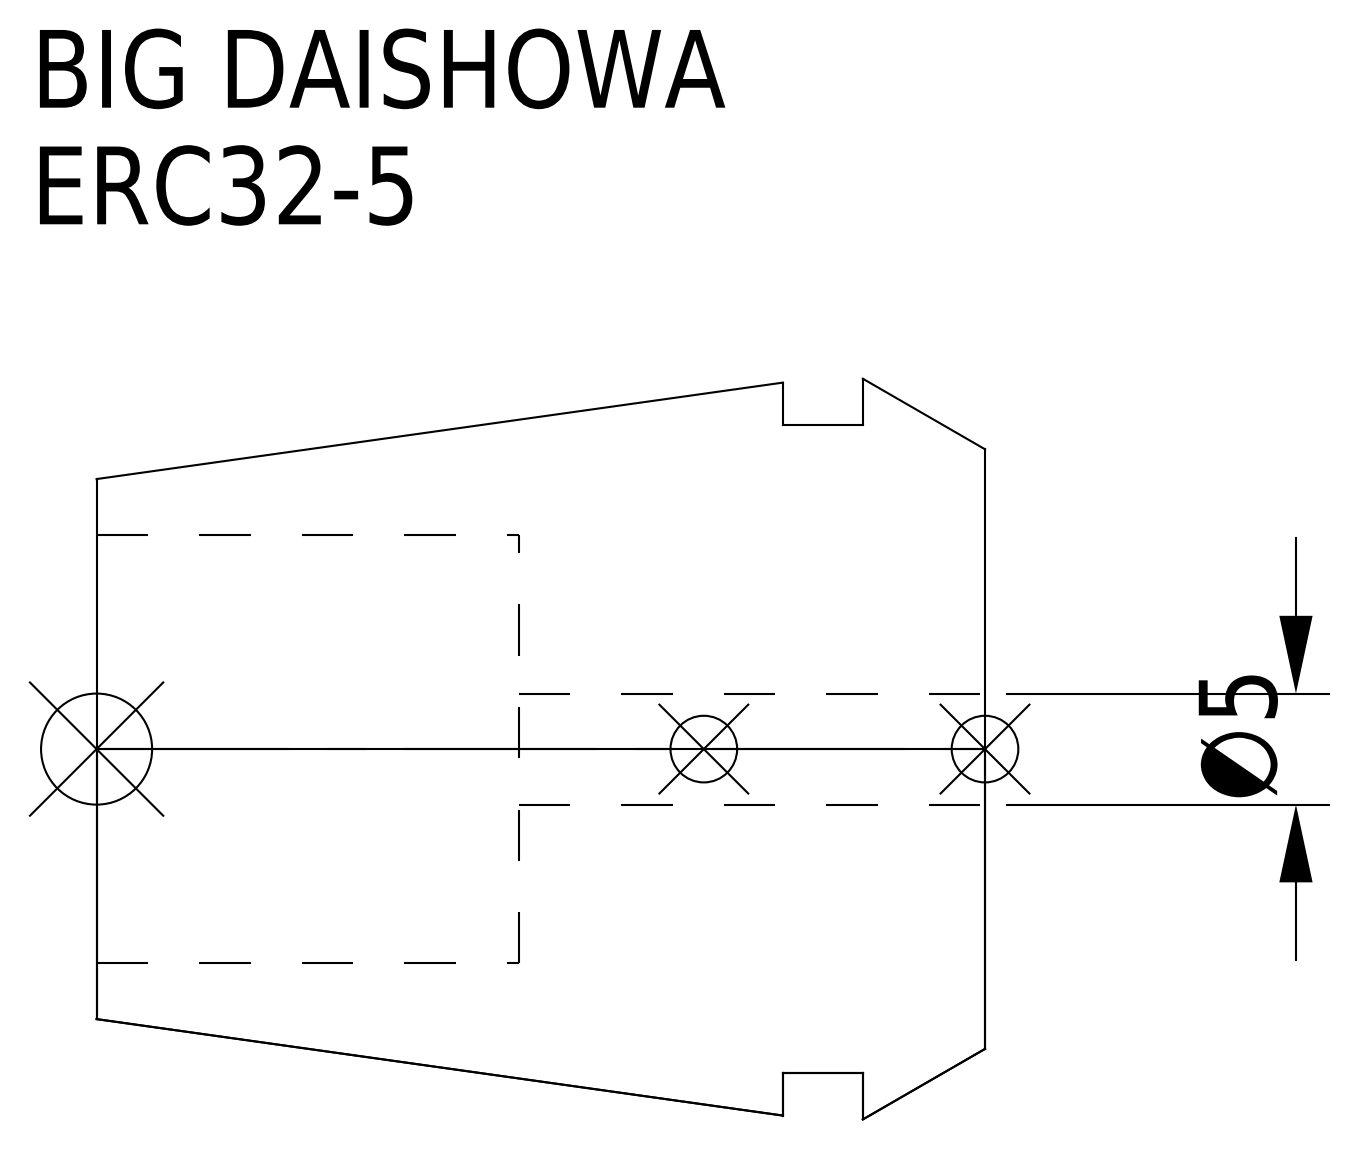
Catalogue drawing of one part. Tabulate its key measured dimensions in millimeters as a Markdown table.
| quantity | value |
| --- | --- |
| part name | ERC32-5 |
| STEP written by | CREO PARAMETRIC BY PTC INC, 2016380 (AUTOMOTIVE_DESIGN) |
| units | millimeters |
| bodies | 1 solid, 15 faces (5 planar, 6 cylindrical, 4 other) |
| overall size | 40 × 33.35 × 33.35 |
| volume | 20 472 mm³ |
| surface area | 6 611 mm² |
| round holes (diameter × count) | 5 × 1, 19.3 × 1 |
| round bosses / shafts (diameter × count) | 29.2 × 1 |
| main face-to-face distances | 21, 5.5, 15.5, 9.1, 3.6, 11.9, 40, 34.5, 30.9, 19 |
